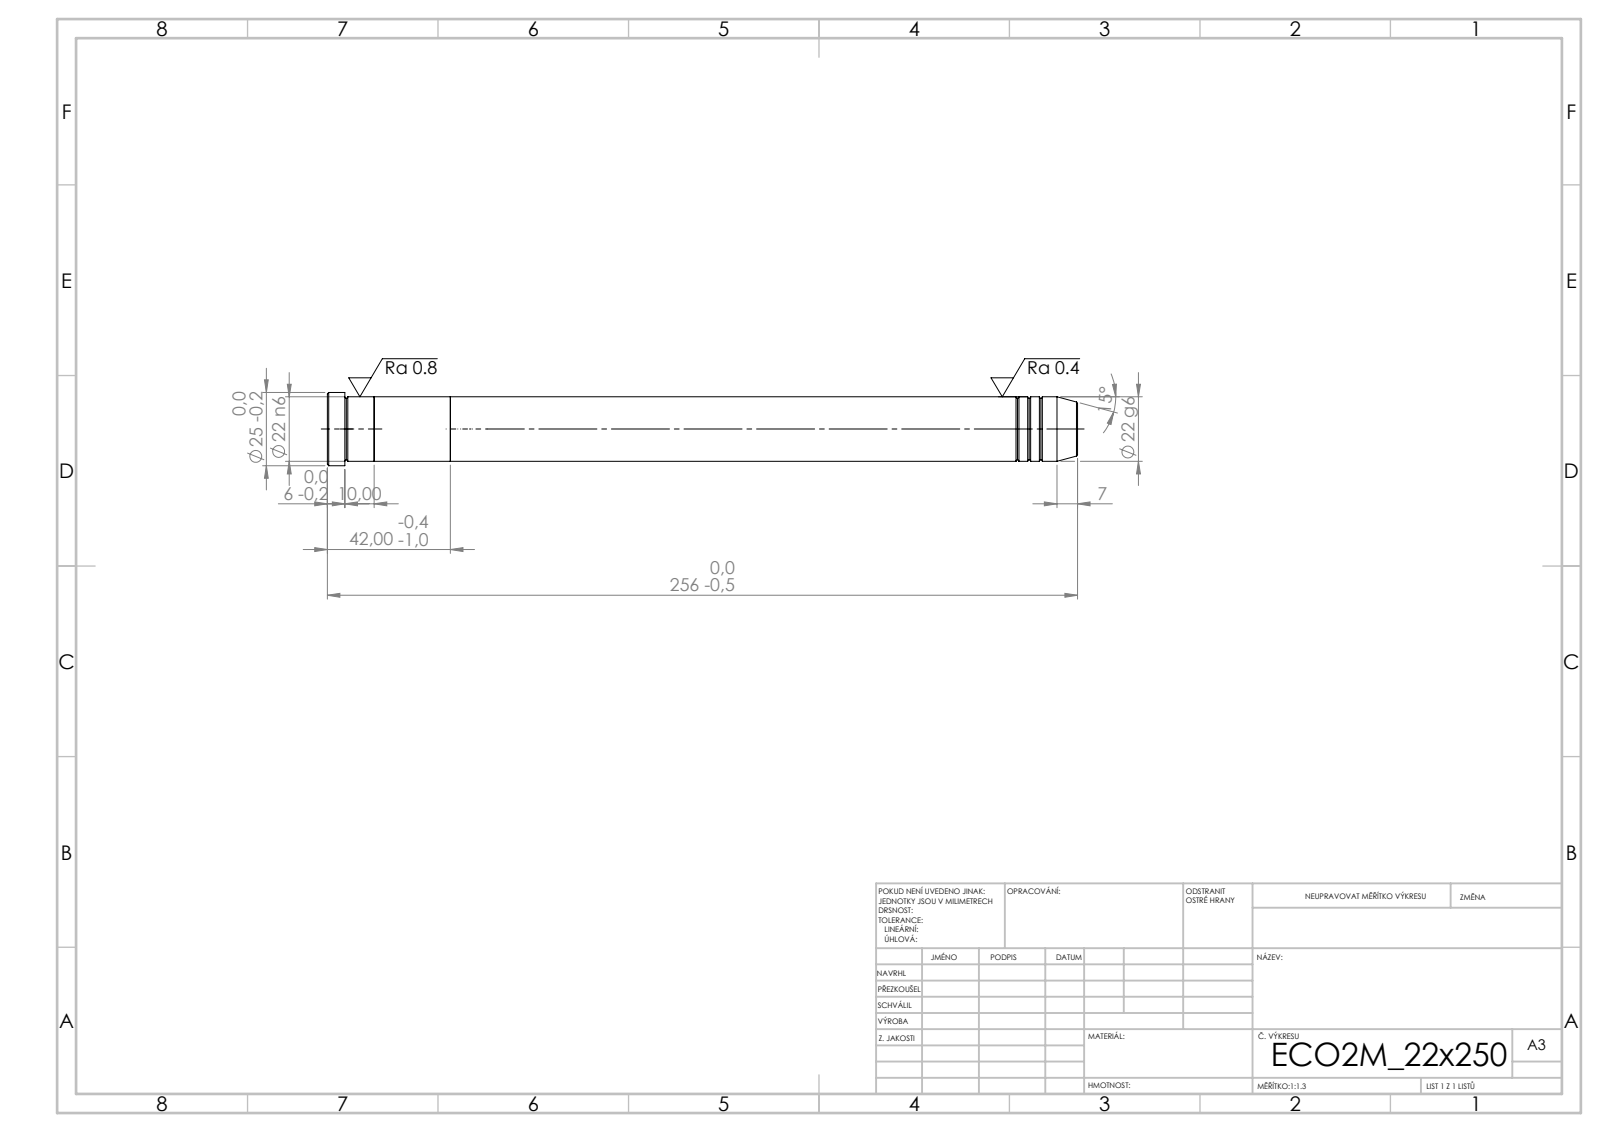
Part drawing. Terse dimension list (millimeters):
written by: SolidWorks 2019 (CONFIG_CONTROL_DESIGN)
unit: mm
bodies: 3 solids, 43 faces (7 planar, 14 cylindrical, 22 other)
size: 256 × 25 × 25
volume: 97 433 mm³; area: 20 223 mm²
bosses: 1× ⌀25, 1× ⌀22
face distances: 26, 42, 16, 214, 240, 256, 250, 36, 10, 6
